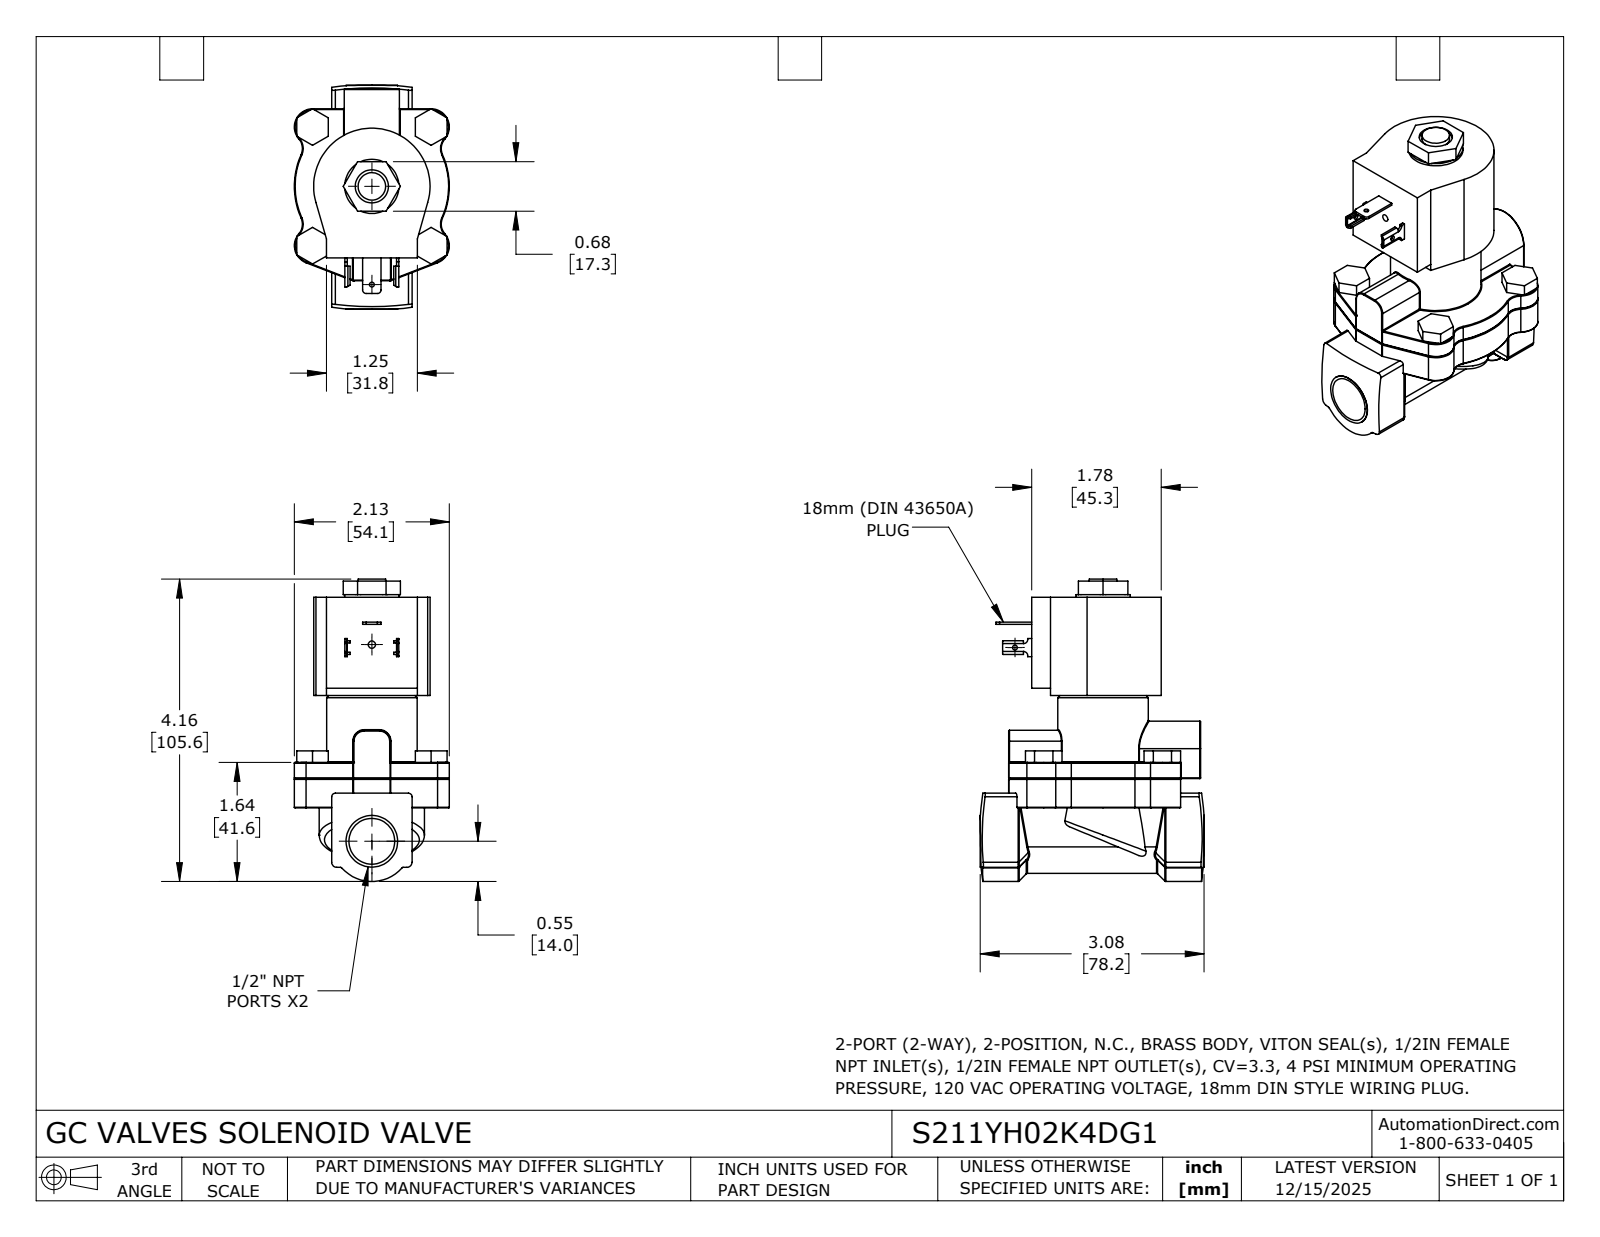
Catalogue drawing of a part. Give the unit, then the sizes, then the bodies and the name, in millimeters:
Units: millimetres
Overall size (bounding box): 105.6 × 78.2 × 54.1
Round holes (diameter × count): ⌀1.7 ×1, ⌀1.7 ×1, ⌀2.5 ×1, ⌀11.6 ×1, ⌀16 ×1
Round bosses / shafts (diameter × count): ⌀31.6 ×1, ⌀18.9 ×1, ⌀18 ×1, ⌀9.6 ×1
Partial cylindrical surfaces — rounded edges, fillets, slot ends (radius × count): R0.3 ×32, R0.5 ×14, R0.2 ×4, R1 ×4, R1.3 ×4, R2.5 ×4, R5.1 ×4, R6.4 ×4
Main face-to-face distances: 57.7, 15.9, 73.5, 39.2, 23.4, 34.3, 28.1, 19.9, 4.1, 19.3
Hole centre spacings: 34.3, 68.7
Volume: 168 600 mm³ · Surface area: 28 280 mm²
Bodies: 1 solid, 447 faces (159 planar, 149 cylindrical, 139 other)
Part name (STEP PRODUCT): S211YH02K4DG1
STEP written by: SolidWorks 2024 (CONFIG_CONTROL_DESIGN)
